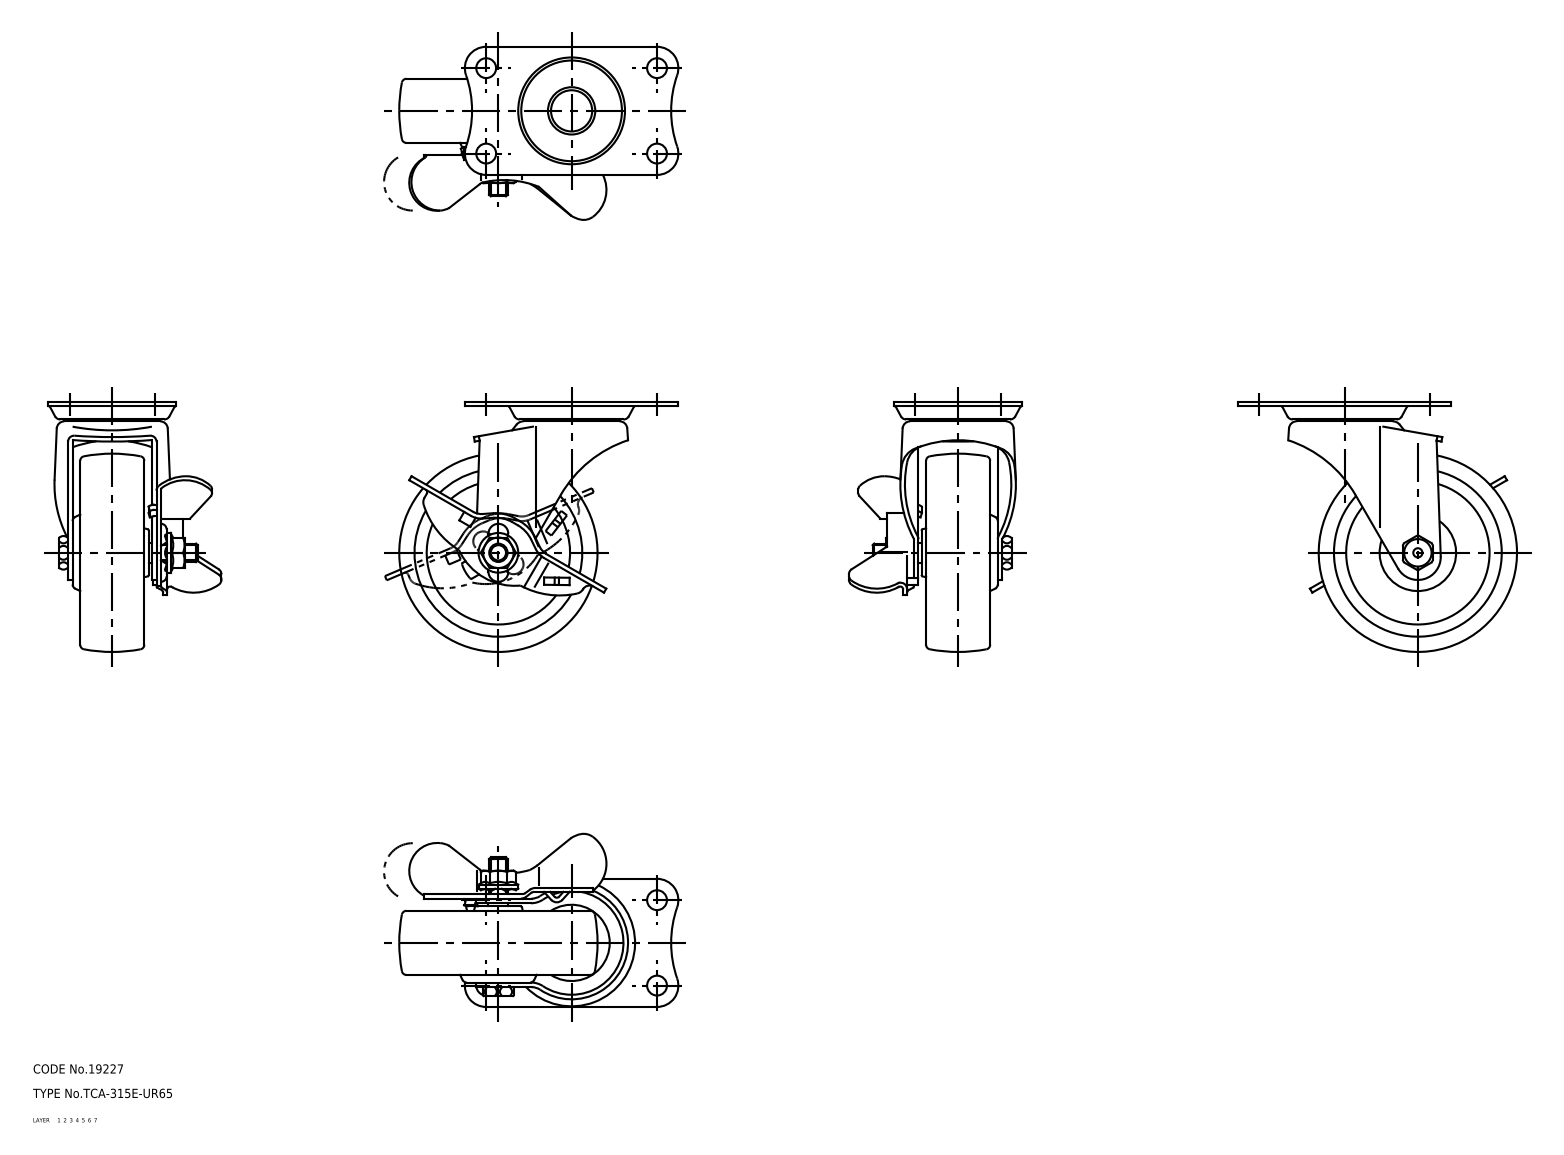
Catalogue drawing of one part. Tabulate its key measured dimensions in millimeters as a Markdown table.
| quantity | value |
| --- | --- |
| part name | axle; wheel; mounting plate; main shaft (+2 more) |
| STEP written by | CADfix (AUTOMOTIVE_DESIGN) |
| units | millimeters |
| bodies | 8 solids, 512 faces (0 planar, 0 cylindrical, 512 other) |
| overall size | 91.5 × 82 × 56.75 |
| volume | 72 540 mm³ |
| surface area | 37 034 mm² |
